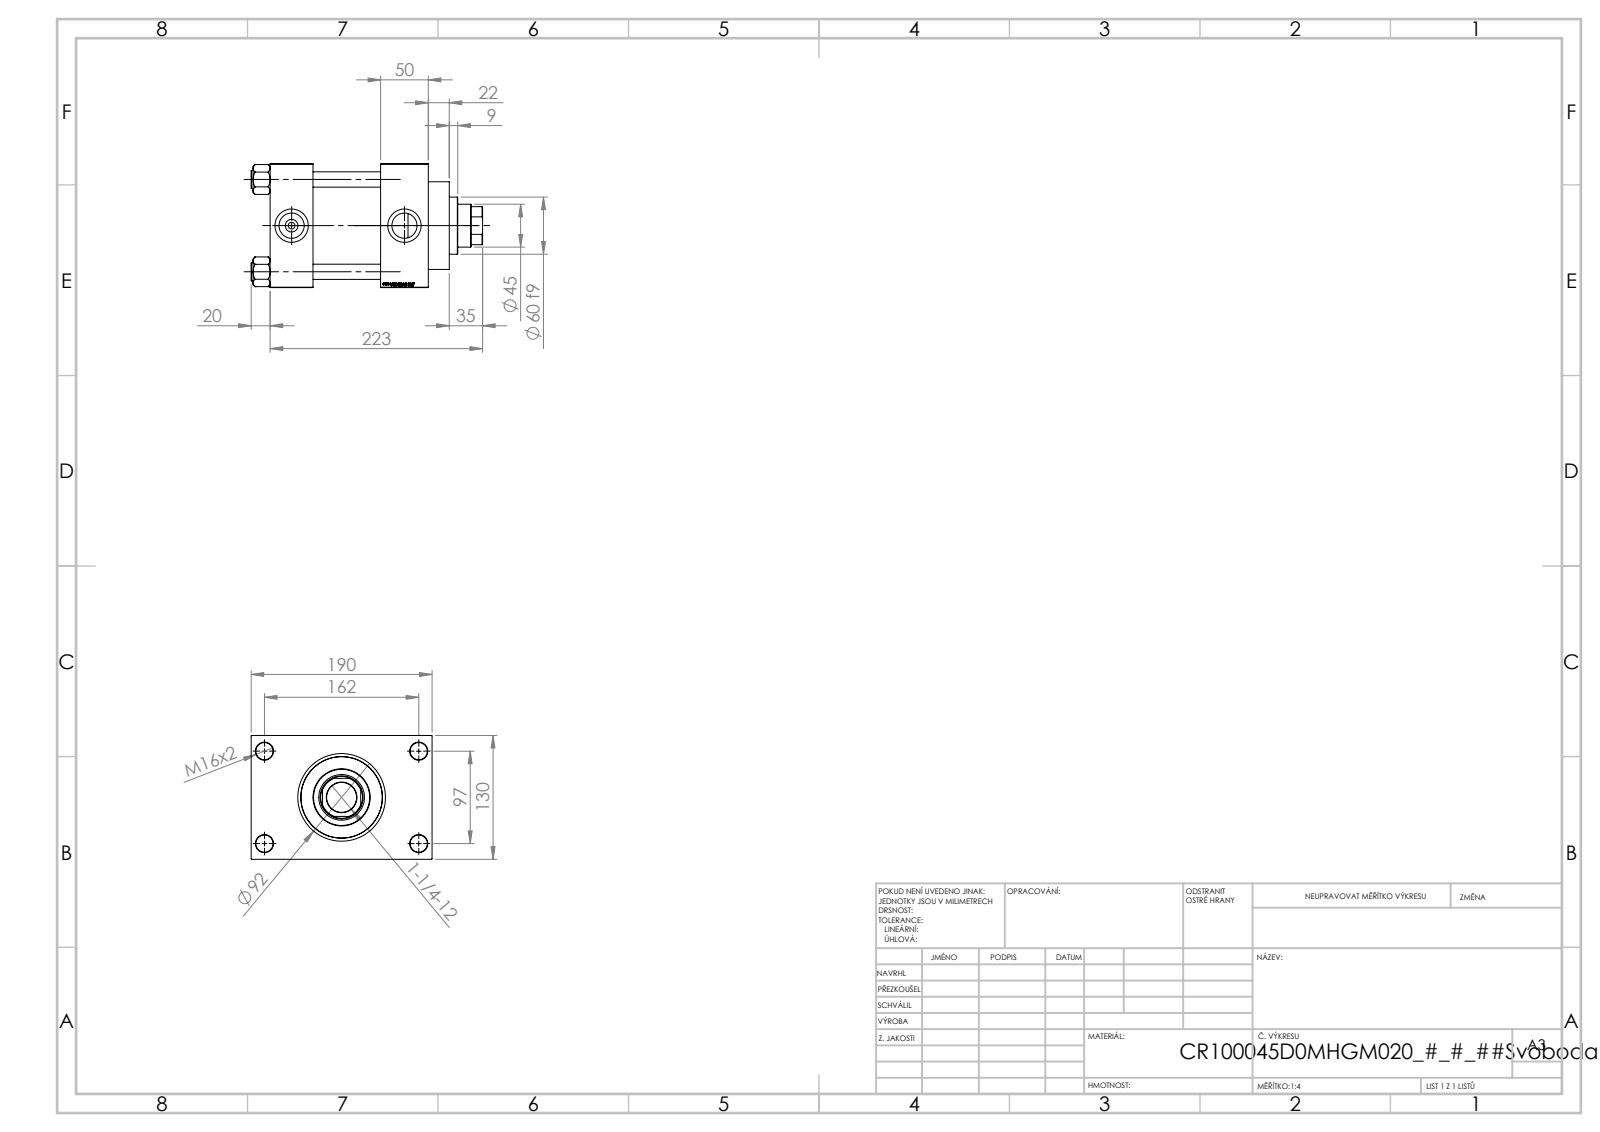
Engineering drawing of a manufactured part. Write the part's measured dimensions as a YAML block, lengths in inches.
part_name: "V215CR_D_TYCINKA; V215CR_VCP_D; V215CR_D_Body; NUT_M5_D (+1 more)"
step_written_by: "SolidWorks 2019 (CONFIG_CONTROL_DESIGN)"
units: inches
bodies: {solids: 11, faces: 1151, planar: 545, cylindrical: 88, other: 518}
overall_size: [9.567, 7.48, 5.118]
volume: 158.1
surface_area: 550.1
round_holes:
  - {diameter: 0.63, count: 4}
  - {diameter: 0.709, count: 4}
  - {diameter: 0.276, count: 2}
  - {diameter: 1.041, count: 2}
  - {diameter: 1.378, count: 2}
  - {diameter: 1.24, count: 1}
  - {diameter: 1.772, count: 1}
  - {diameter: 1.89, count: 1}
  - {diameter: 2.992, count: 1}
  - {diameter: 3.366, count: 1}
  - {diameter: 3.937, count: 1}
round_bosses_or_shafts:
  - {diameter: 0.748, count: 4}
  - {diameter: 4.173, count: 1}
  - {diameter: 3.622, count: 1}
  - {diameter: 2.362, count: 1}
partial_cylinders:
  - {radius: 0.866, count: 1}
face_to_face_distances: [5.118, 1.772, 4.567, 2.795, 6.535, 4.764, 1.969, 1.181, 6.299, 0.787]
hole_center_spacings: [1.281, 2.698, 3.717, 3.815, 4.026, 5.096, 6.367, 3.819]
